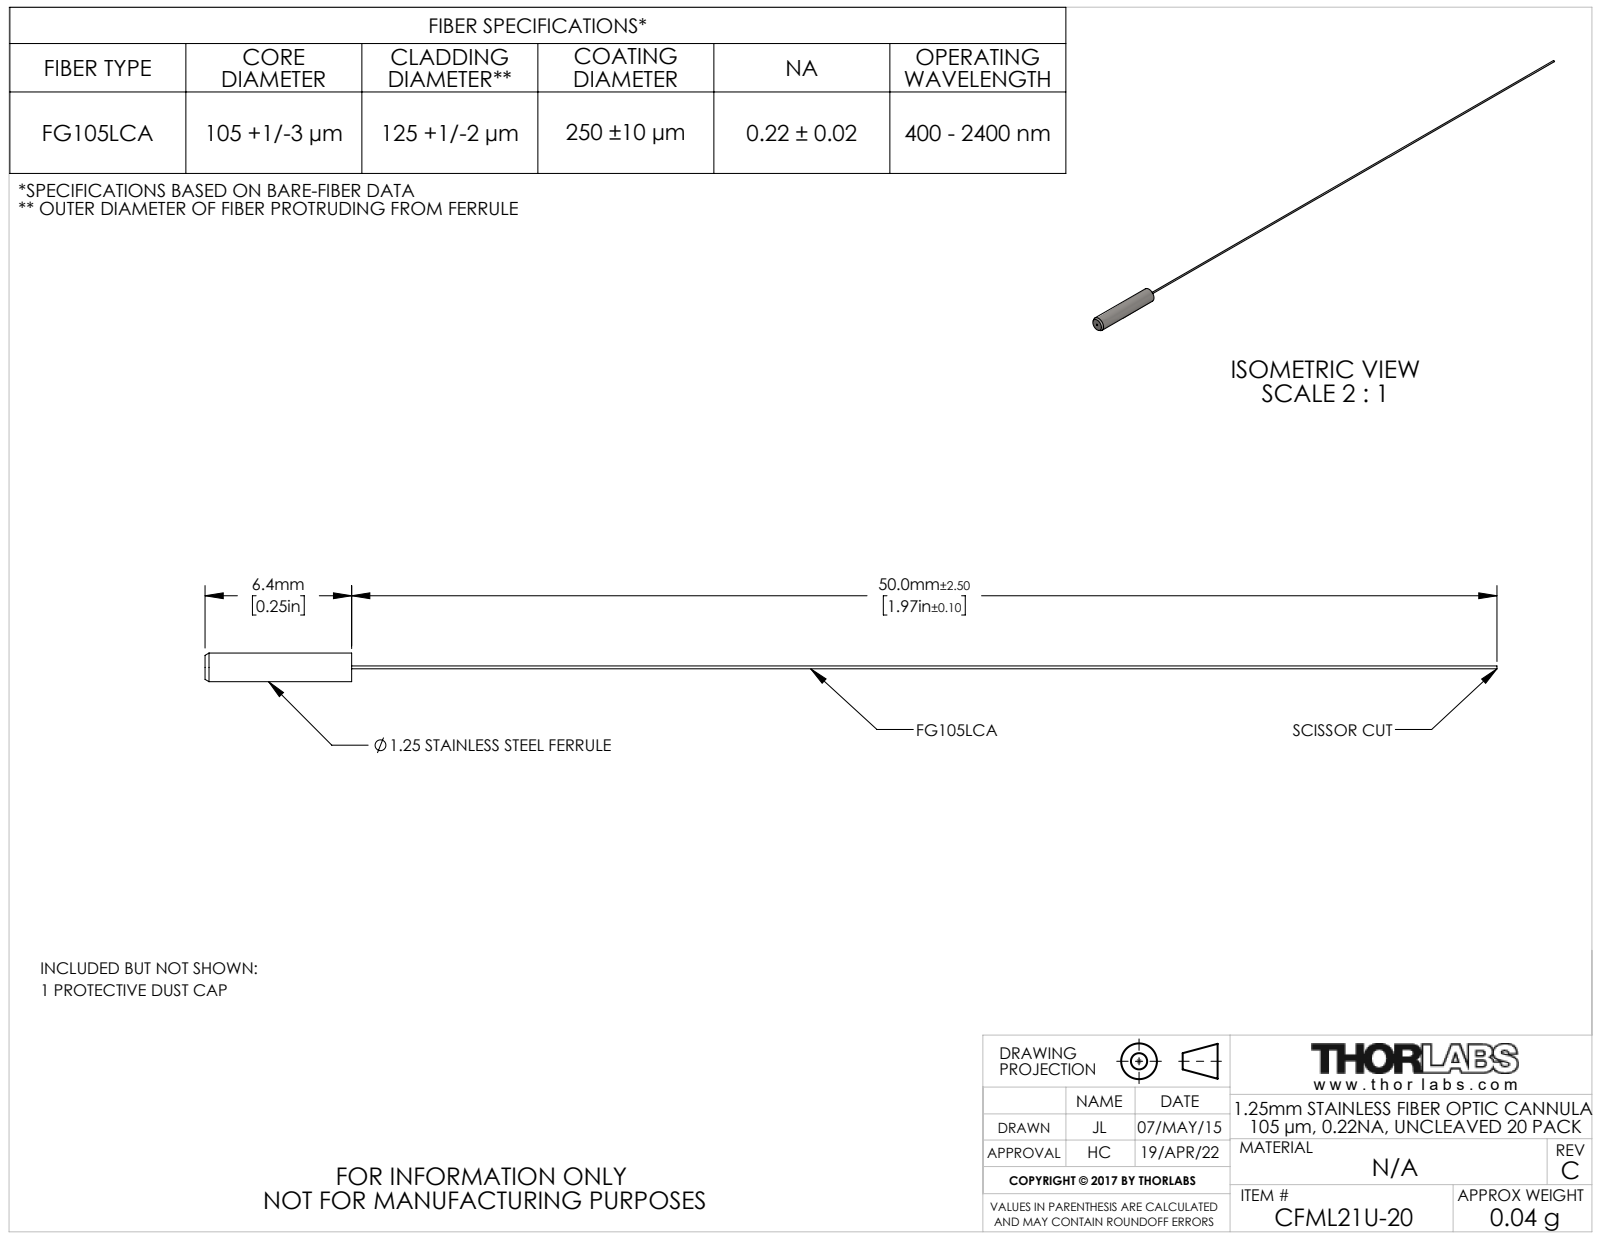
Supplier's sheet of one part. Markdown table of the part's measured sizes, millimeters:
| quantity | value |
| --- | --- |
| part name | TTN041718-E0W |
| STEP written by | SolidWorks 2014 (CONFIG_CONTROL_DESIGN) |
| units | millimeters |
| bodies | 2 solids, 18 faces (4 planar, 8 cylindrical, 6 other) |
| overall size | 56.4 × 1.2 × 1.2 |
| round holes (diameter × count) | 1 × 1 |
| round bosses / shafts (diameter × count) | 1.2 × 1 |
| main face-to-face distances | 6.4, 56.4, 50 |
